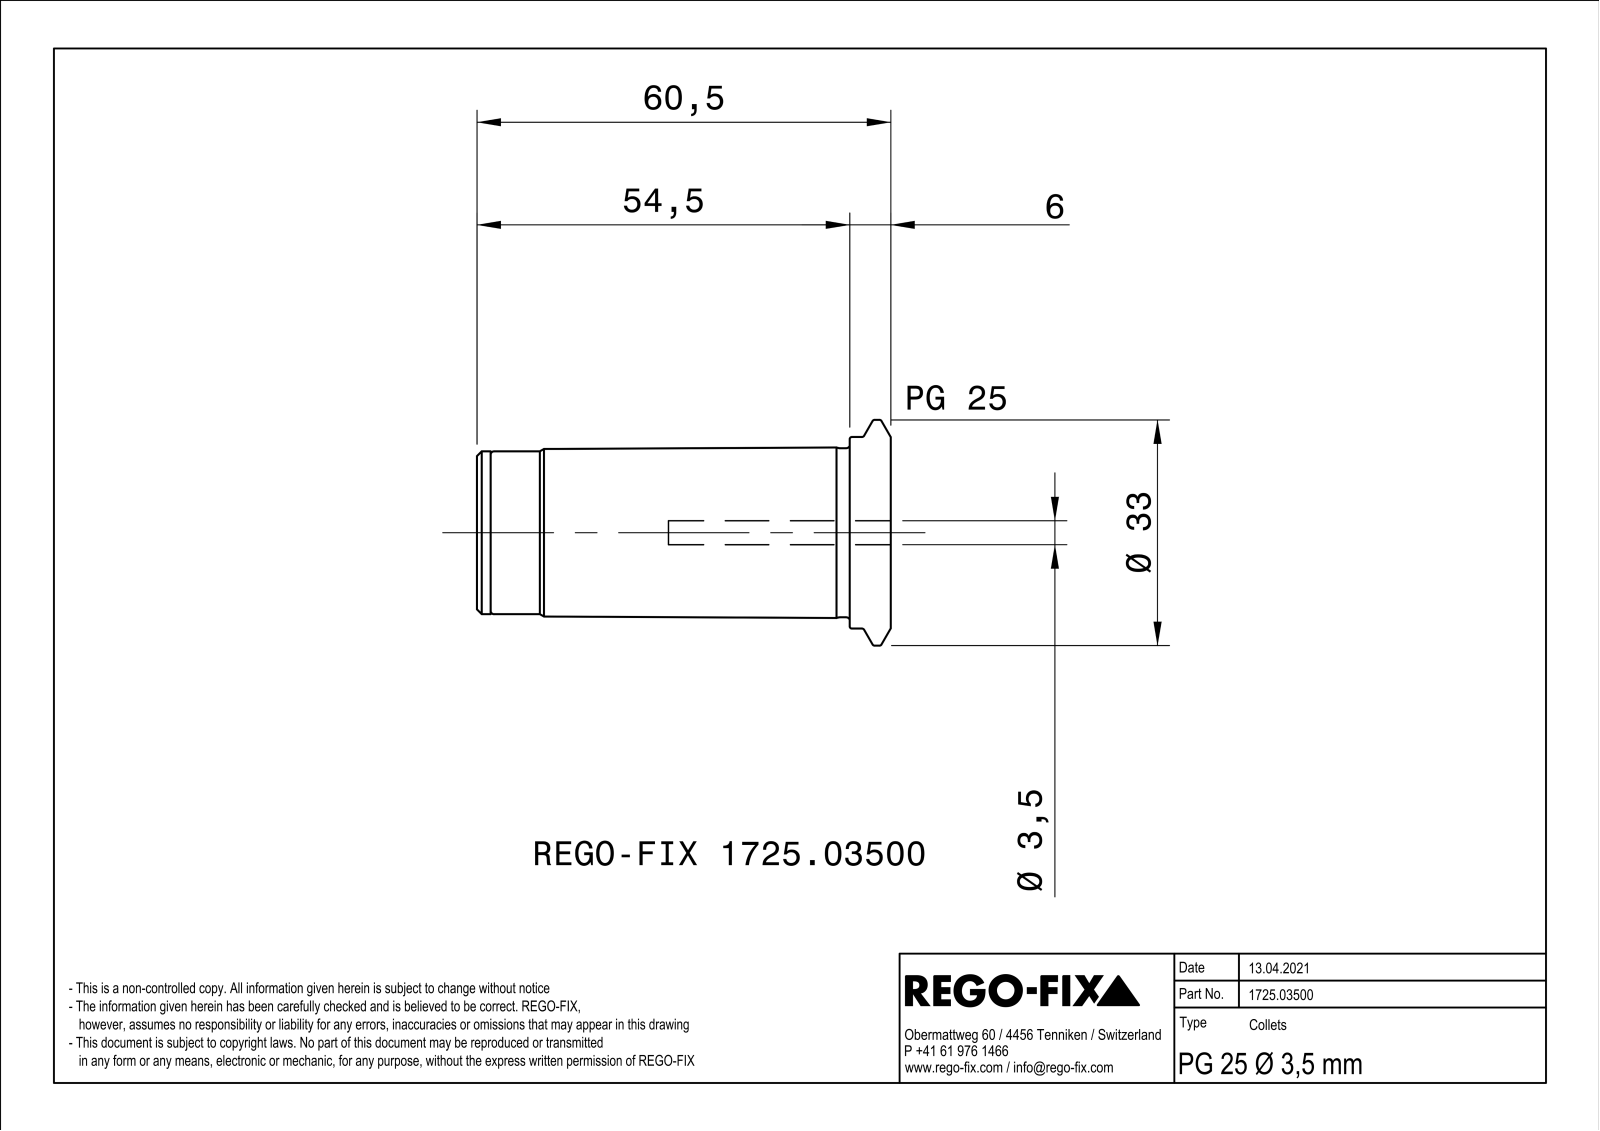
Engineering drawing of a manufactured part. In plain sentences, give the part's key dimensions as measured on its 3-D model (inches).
The part is named "NOCUT". Its 3-D file was written by "SIEMENS PLM Software Solid Edge ST10 (AUTOMOTIVE_DESIGN)". It is 1 solid with 89 faces: 23 planar, 25 cylindrical and 41 other. Overall it measures 2.382 by 1.299 by 1.299 inches. Round holes: 3 of diameter 0.098, 1 of diameter 0.138, 1 of diameter 0.197, 1 of diameter 0.205, 1 of diameter 0.272, 1 of diameter 0.323, 1 of diameter 0.354, 1 of diameter 0.803, 1 of diameter 0.824, 1 of diameter 0.874. Round bosses or shafts: 1 of diameter 1.299, 1 of diameter 1.102, 1 of diameter 0.972, 1 of diameter 0.937, 1 of diameter 0.472. The main face-to-face distances are 0.039, 2.382, 2.071, 0.311, 2.303, 0.232, 0.079, 1.969, 0.102, 0.335. The hole center spacings are 0.305, 0.529, 0.528.
